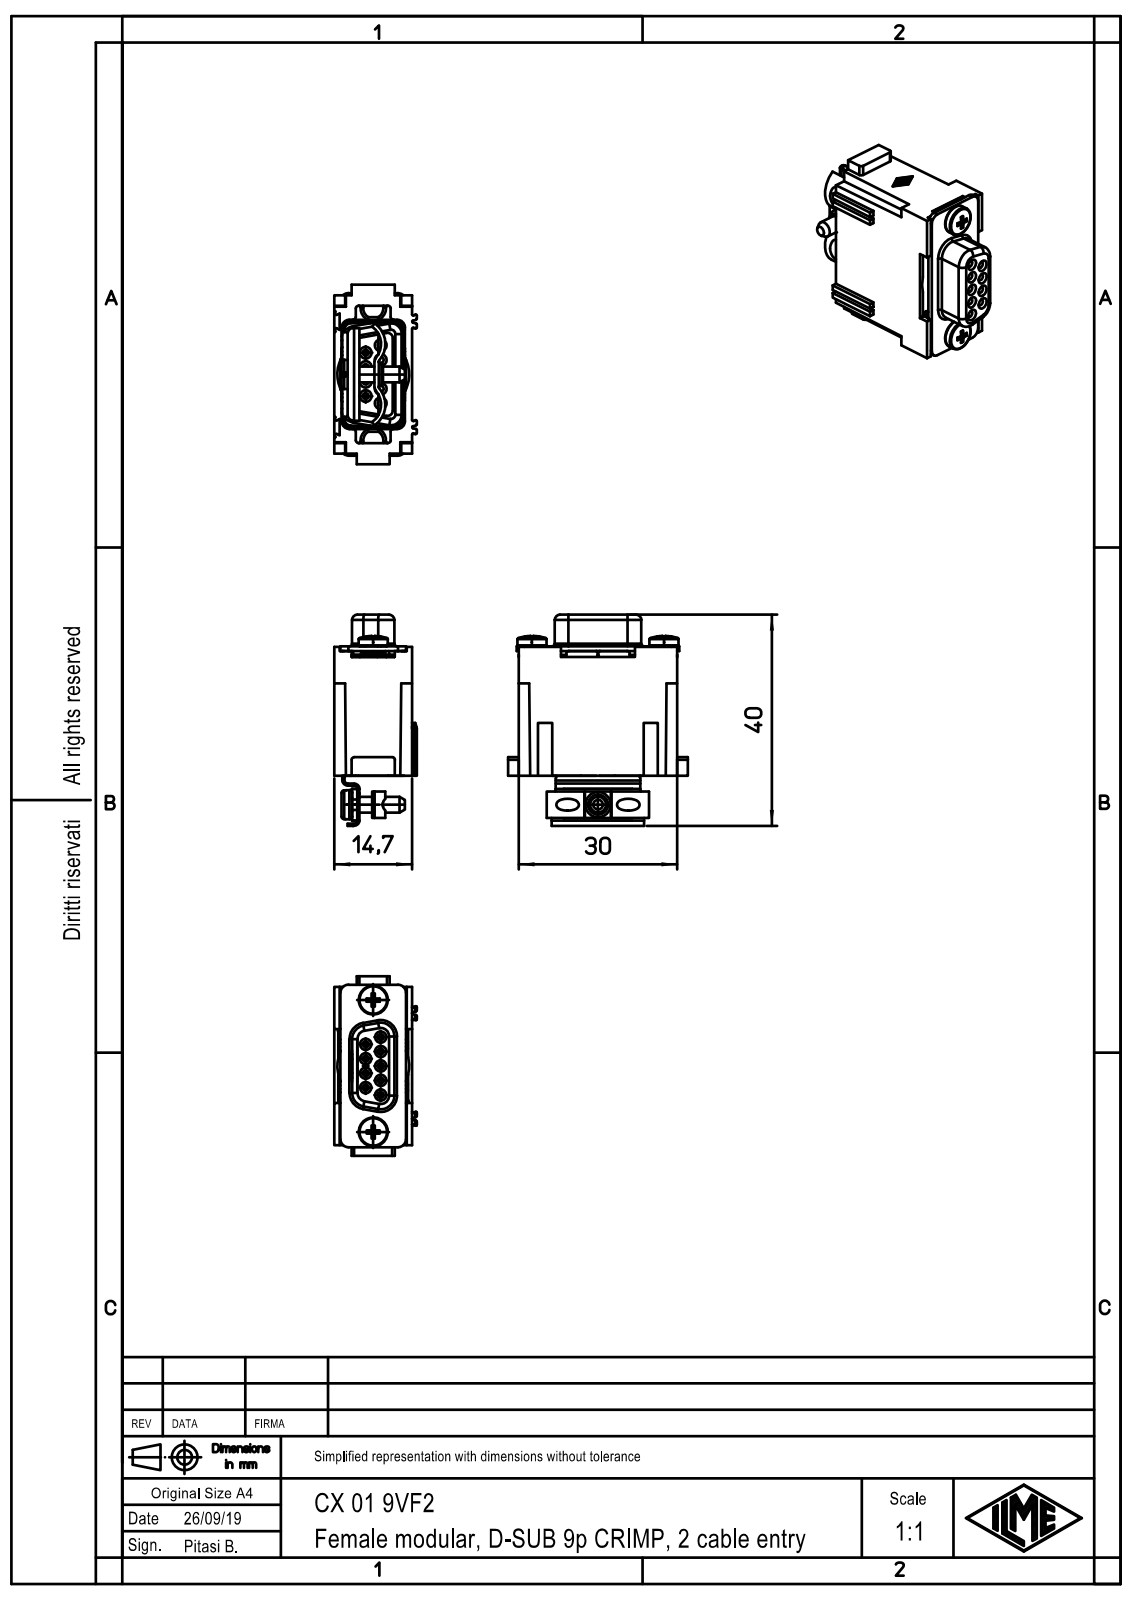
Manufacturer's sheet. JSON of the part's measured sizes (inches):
{"part_name": "CX 01 9VF2", "step_written_by": "Creo Elements/Direct Modeling 20.1B 02-Apr-2019 (C) Parametric Technology GmbH (AUTOMOTIVE_DESIGN)", "units": "inches", "bodies": {"solids": 1, "faces": 304, "planar": 172, "cylindrical": 98, "other": 34}, "overall_size": [1.575, 1.339, 0.614], "volume_in3": 0.71, "surface_area_in2": 7.522, "round_holes": [[0.045, 9], [0.089, 9], [0.094, 1], [0.126, 1]], "round_bosses_or_shafts": [[0.217, 3], [0.15, 1], [0.118, 1], [0.102, 1]], "partial_cylinders_radius": [[0.039, 15], [0.012, 4], [0.02, 4], [0.059, 4], [0.079, 4], [0.102, 4], [0.024, 3], [0.008, 2]], "face_to_face_distances": [0.579, 1.181, 0.965, 0.079, 0.132, 0.447, 0.039, 0.035, 1.102, 0.081], "hole_center_spacings": [0.124, 0.197, 0.108, 0.292, 0.216, 0.108, 0.124, 0.216]}
